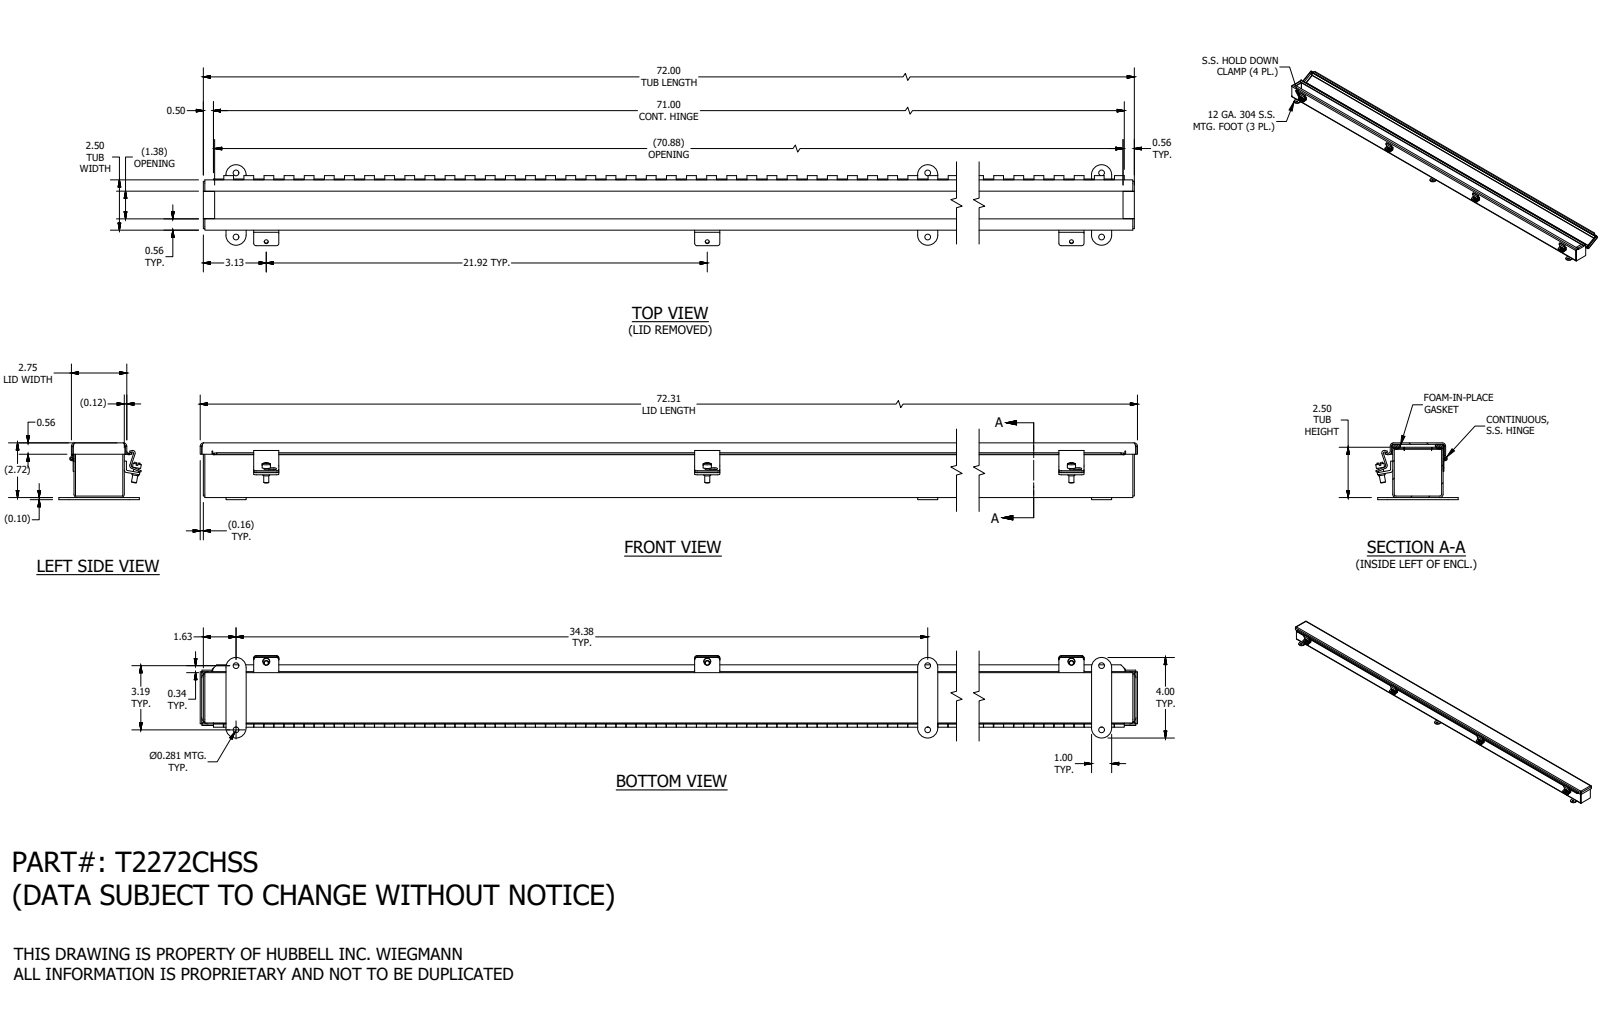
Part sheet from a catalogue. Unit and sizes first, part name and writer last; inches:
Units: inches
Overall size (bounding box): 72.313 × 4.098 × 2.822
Round holes (diameter × count): ⌀0.11 ×8, ⌀0.281 ×6, ⌀0.196 ×4, ⌀0.116 ×1
Round bosses / shafts (diameter × count): ⌀0.41 ×4, ⌀0.344 ×4, ⌀0.25 ×4, ⌀0.2 ×1, ⌀0.1 ×1
Partial cylindrical surfaces — rounded edges, fillets, slot ends (radius × count): R0.125 ×16, R0.094 ×11, R0.168 ×11, R0.085 ×8, R0.133 ×8, R0.5 ×6, R0.242 ×4, R0.063 ×3
Main face-to-face distances: 0.074, 2.426, 2.644, 2.5, 2.352, 2.718, 2.57, 0.218, 2.552, 0.126
Hole centre spacings: 21.917, 0.75, 34.375, 34.522, 43.833, 3.187, 21.167, 21.917
Volume: 85.52 in³ · Surface area: 2 270 in²
Bodies: 23 solids, 1144 faces (685 planar, 413 cylindrical, 46 other)
Part name (STEP PRODUCT): T2272CHSS
STEP written by: SolidWorks 2019 (AUTOMOTIVE_DESIGN)
